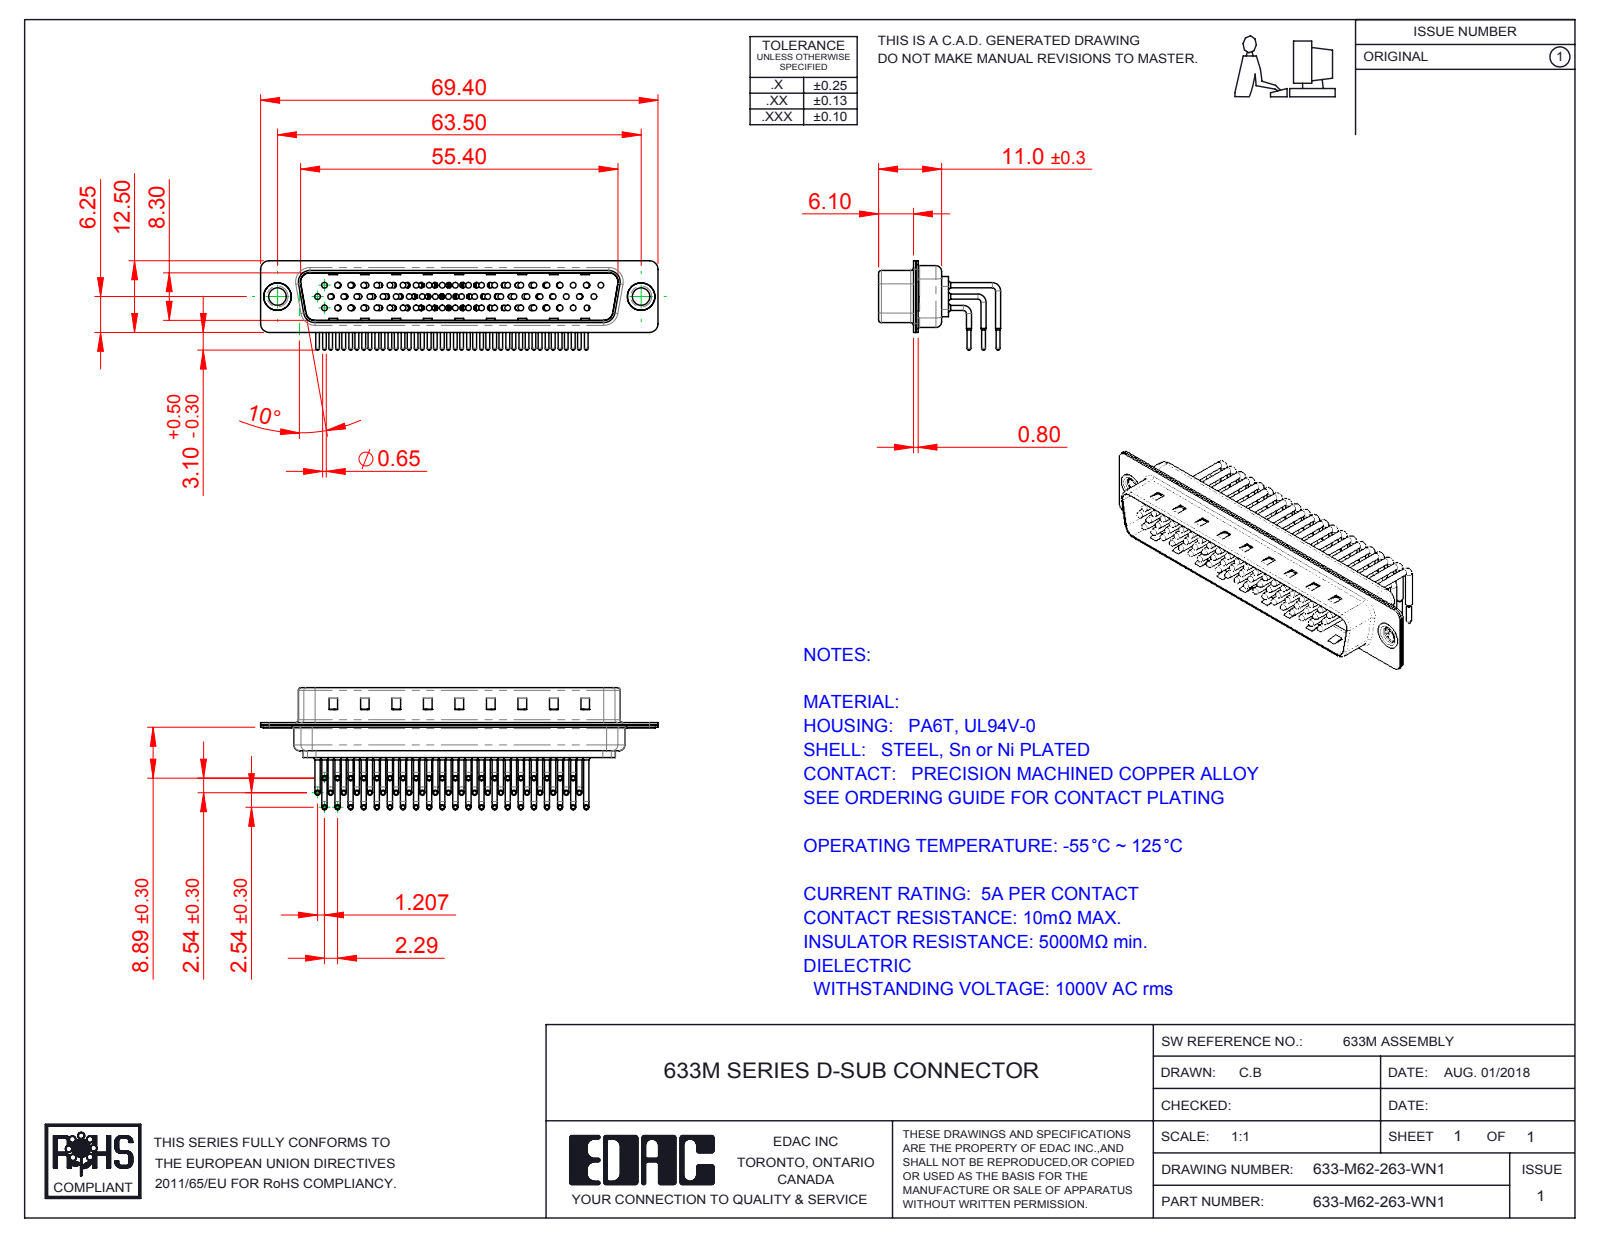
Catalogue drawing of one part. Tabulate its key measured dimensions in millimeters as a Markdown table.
| quantity | value |
| --- | --- |
| part name | 633M Contact Row 2; 633M Housing_62 Contacts; 633M Shell Rear_62 Contacts; 633M Contact Row 1 (+4 more) |
| STEP written by | SolidWorks 2016 (CONFIG_CONTROL_DESIGN) |
| units | millimeters |
| bodies | 67 solids, 7206 faces (4171 planar, 2357 cylindrical, 678 other) |
| overall size | 69.4 × 21.32 × 15.6 |
| volume | 4 269 mm³ |
| surface area | 13 496 mm² |
| round holes (diameter × count) | 1 × 62, 1.7 × 62, 2 × 62, 3.05 × 2, 4 × 2, 4.8 × 2 |
| round bosses / shafts (diameter × count) | 0.9 × 124, 1.5 × 62, 0.65 × 62, 1 × 56, 5 × 2, 4.9 × 2, 3.55 × 2 |
| partial cylindrical surfaces (radius × count) | 1.01 × 62, 1.5 × 16, 2 × 12, 0.5 × 8, 1.6 × 8, 0.25 × 4, 0.6 × 4, 0.65 × 4 |
| main face-to-face distances | 0.4, 0.85, 9.55, 8.7, 1.5, 1.9, 1.25, 10.4, 0.35, 0.45 |
| hole center spacings | 7.24, 2.32, 2.41, 4.13, 9.65, 4.83, 14.48, 11.04 |
